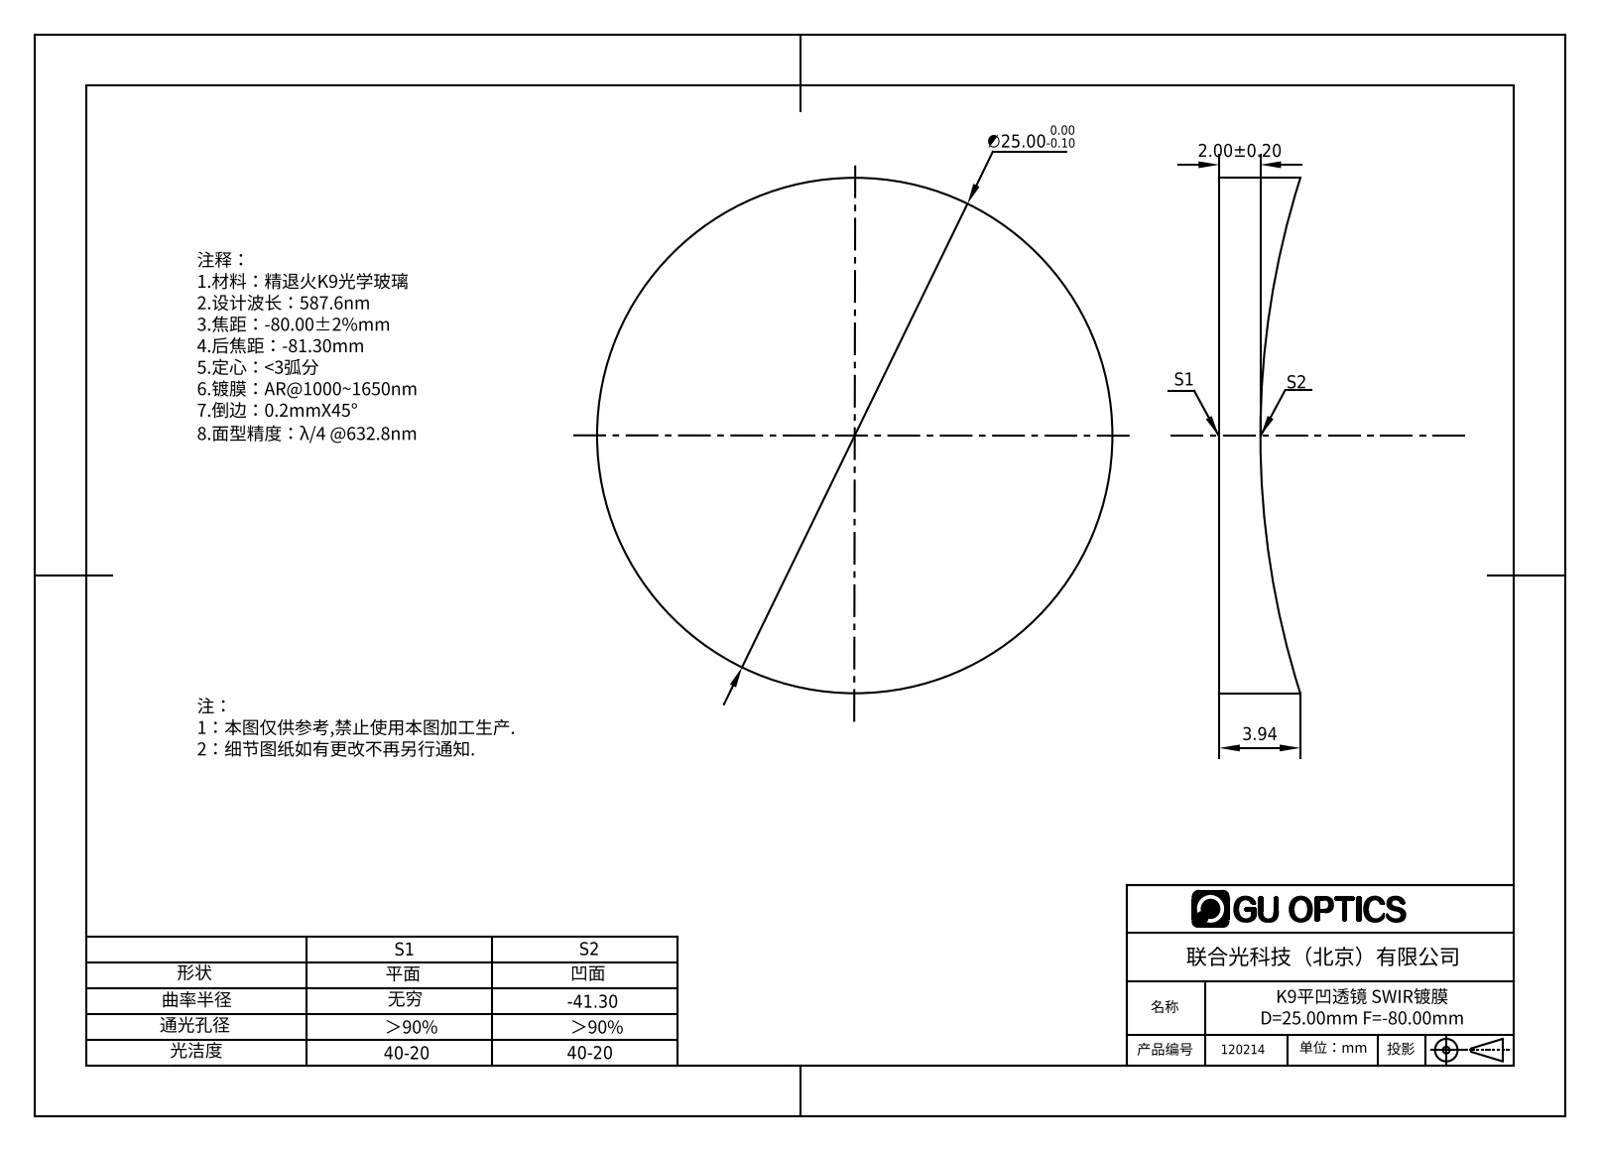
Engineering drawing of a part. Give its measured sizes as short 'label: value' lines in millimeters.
name: 120154
written by: SolidWorks 2016 (AUTOMOTIVE_DESIGN)
unit: mm
bodies: 1 solid, 5 faces (1 planar, 2 cylindrical, 2 other)
size: 25 × 25 × 3.94
volume: 1 454 mm³; area: 1 303 mm²
bosses: 1× ⌀25
